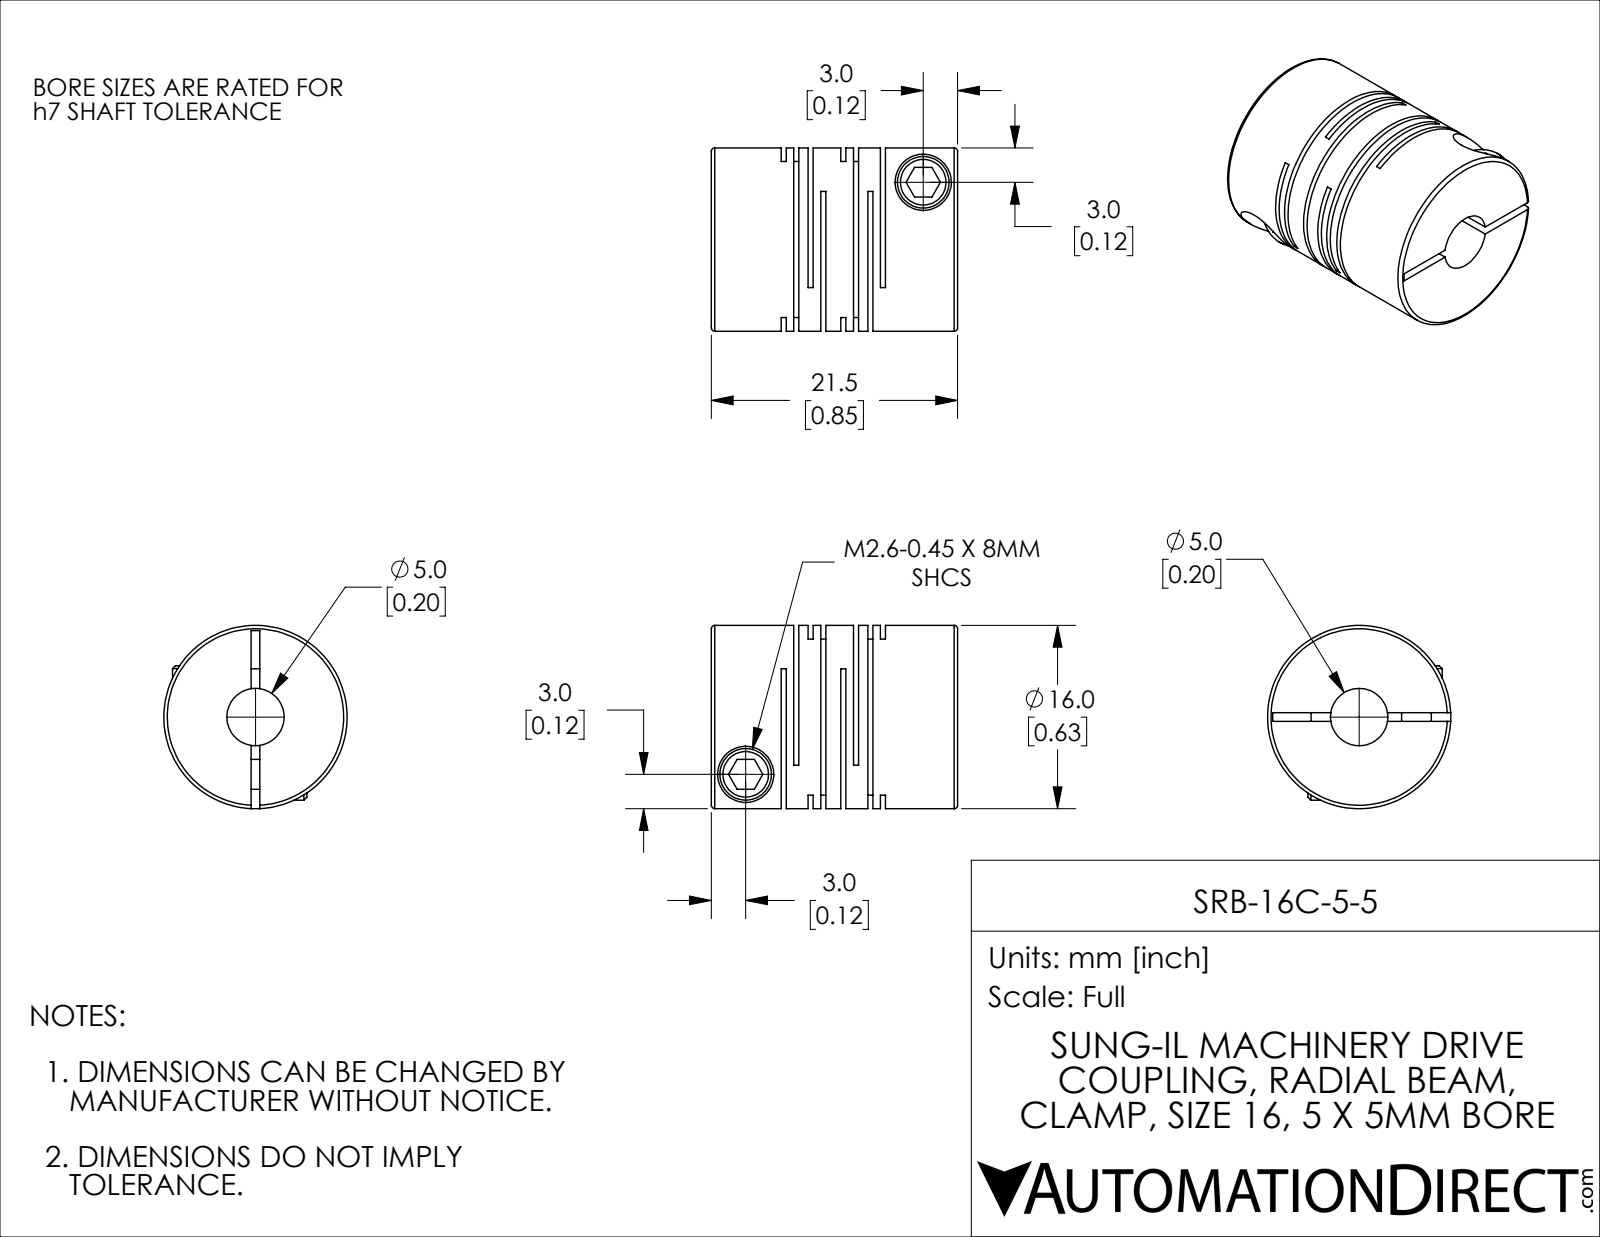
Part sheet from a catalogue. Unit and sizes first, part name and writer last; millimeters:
Units: millimetres
Overall size (bounding box): 21.5 × 16 × 16
Round holes (diameter × count): ⌀2.6 ×2, ⌀4.9 ×2, ⌀5 ×1
Round bosses / shafts (diameter × count): ⌀4.5 ×2, ⌀16 ×1
Main face-to-face distances: 0.44, 1.1, 2.35, 5.21, 0.66, 1.91, 4.77, 1.25, 4.11, 2.86
Volume: 3 199 mm³ · Surface area: 4 365 mm²
Bodies: 1 solid, 114 faces (60 planar, 42 cylindrical, 12 other)
Part name (STEP PRODUCT): SRB-16C-5-5
STEP written by: SolidWorks 2021 (CONFIG_CONTROL_DESIGN)
